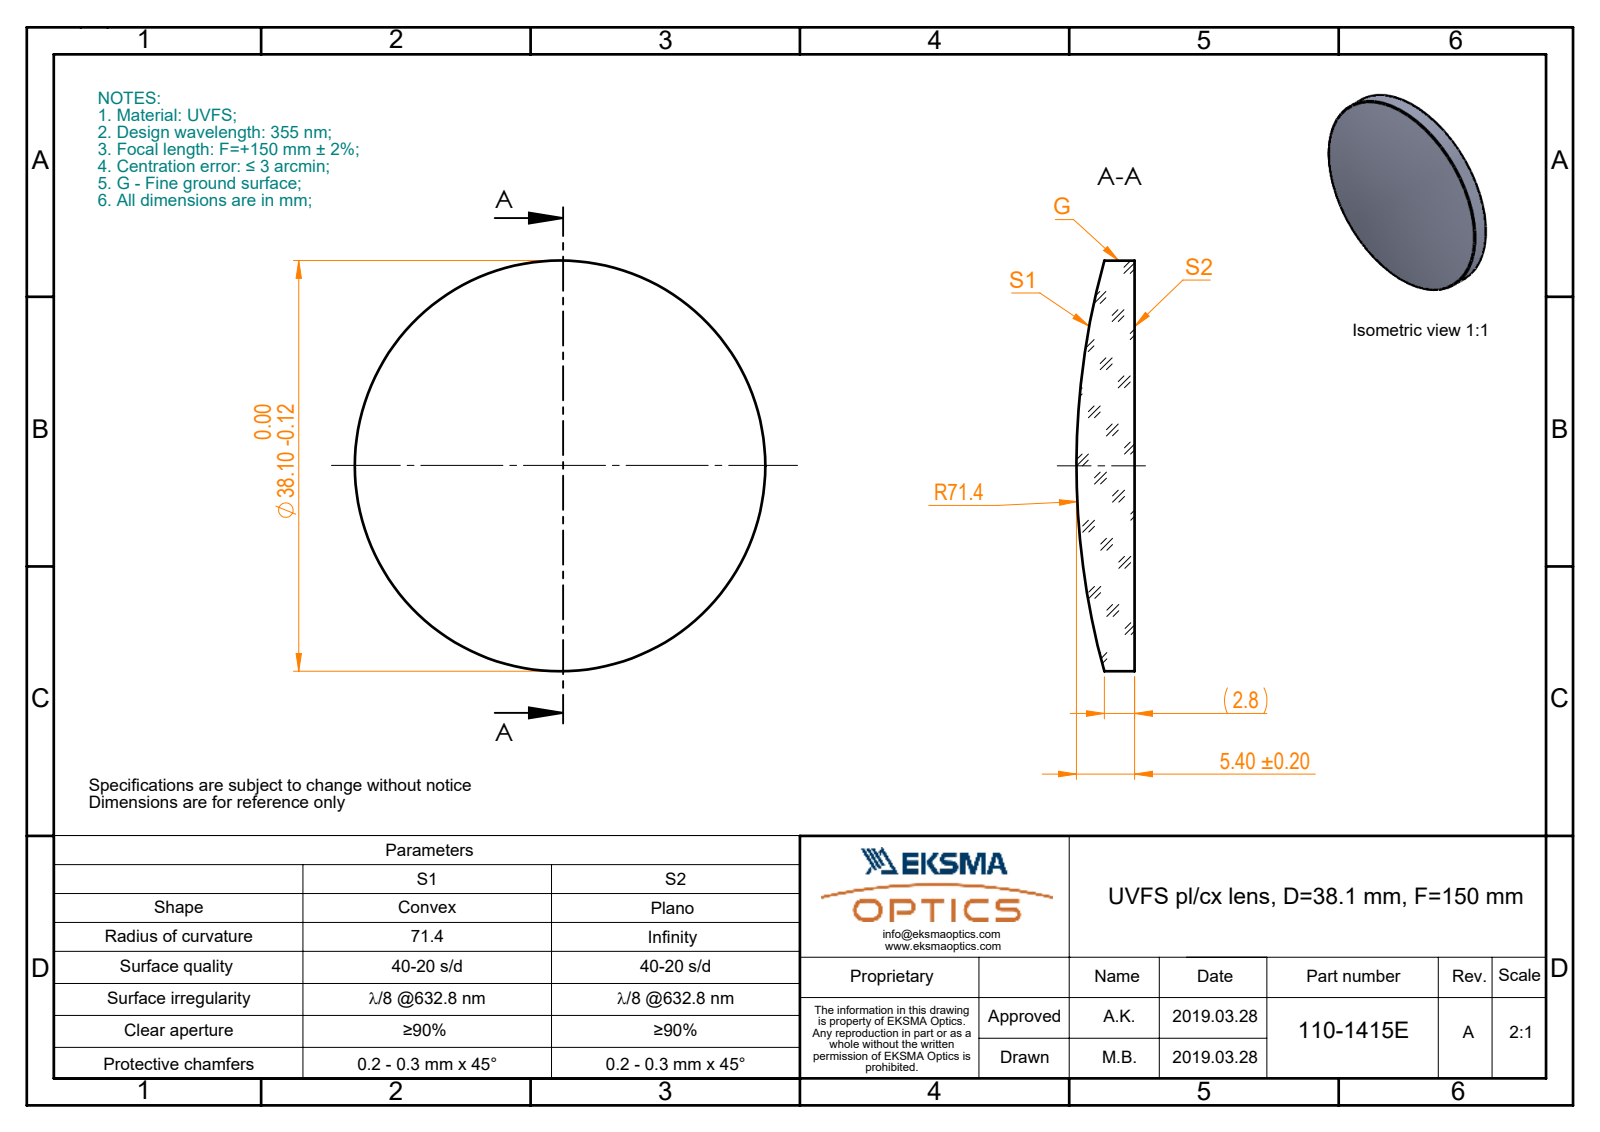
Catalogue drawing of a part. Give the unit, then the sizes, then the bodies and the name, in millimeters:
Units: millimetres
Overall size (bounding box): 38.1 × 38.1 × 5.4
Round bosses / shafts (diameter × count): ⌀38.1 ×1
Volume: 4 690 mm³ · Surface area: 2 638 mm²
Bodies: 1 solid, 5 faces (1 planar, 2 cylindrical, 2 other)
Part name (STEP PRODUCT): 110-1415E UVFS pl-cx 38.1 F150
STEP written by: SolidWorks 2017 (CONFIG_CONTROL_DESIGN)
